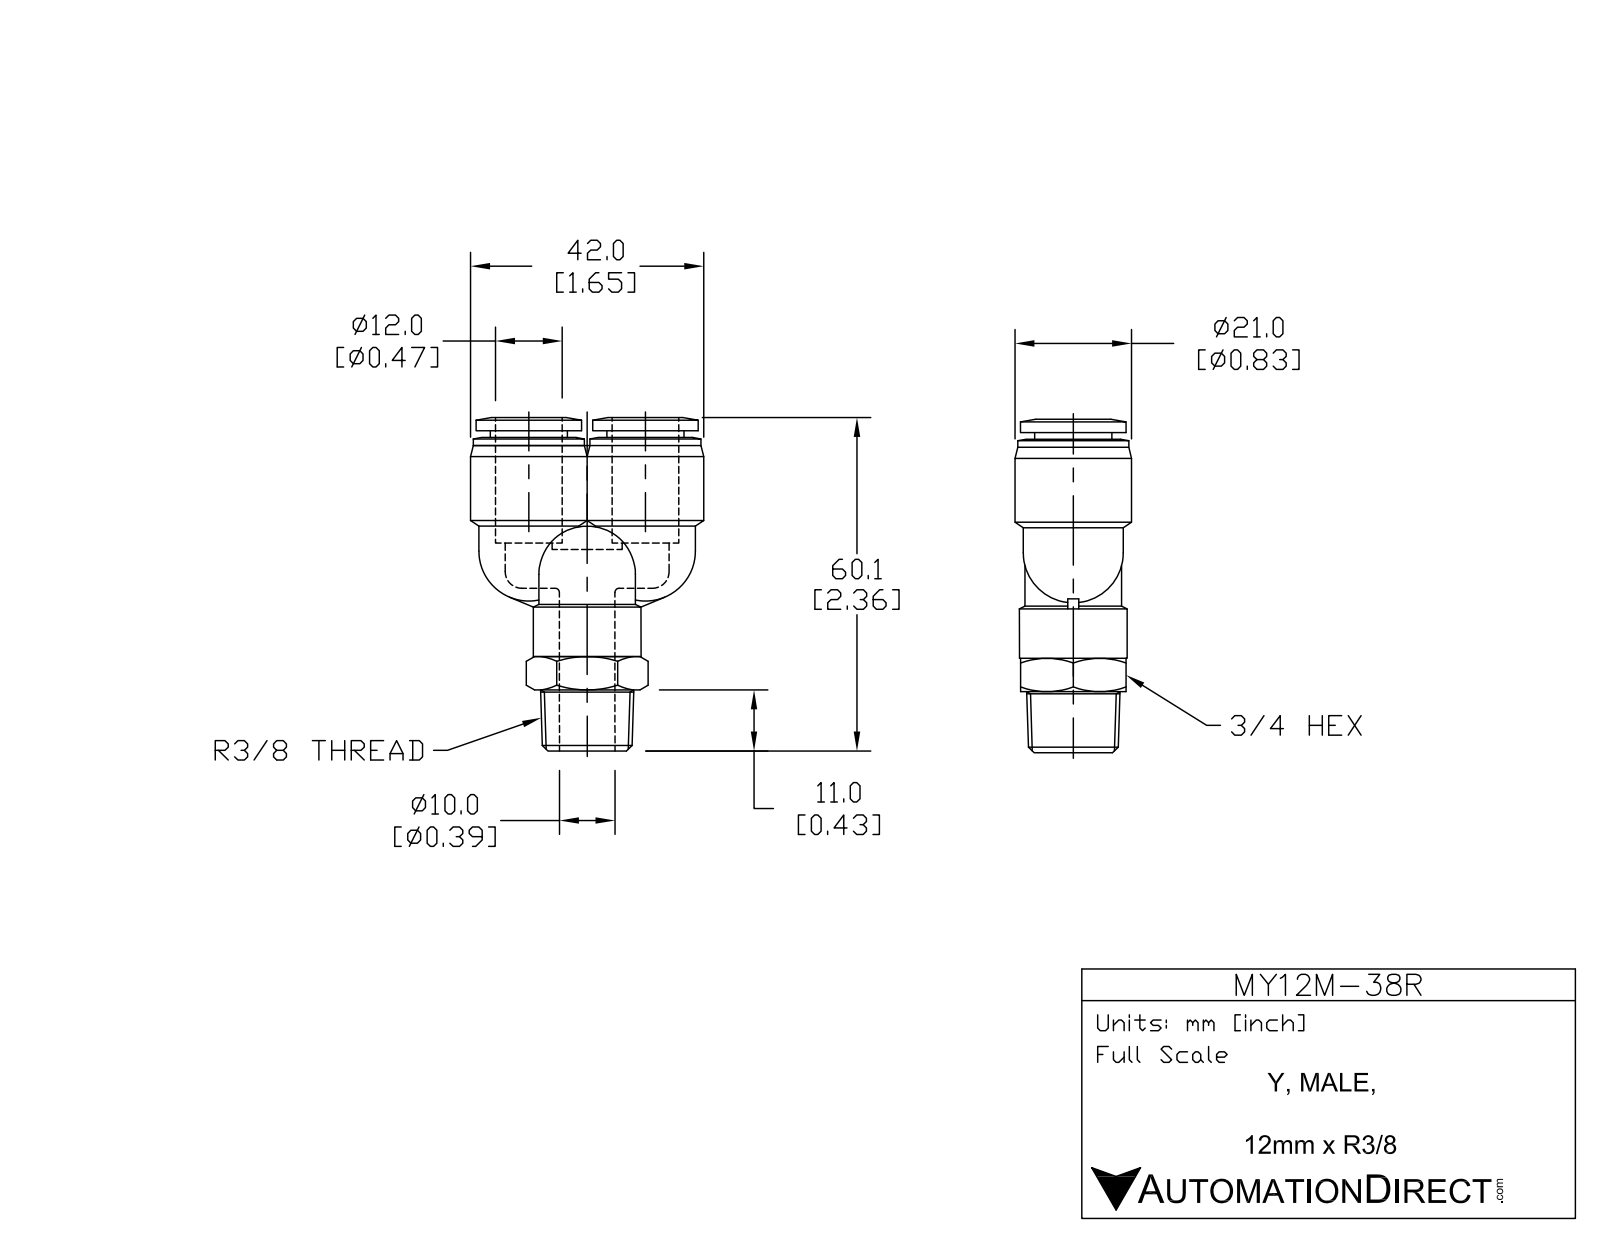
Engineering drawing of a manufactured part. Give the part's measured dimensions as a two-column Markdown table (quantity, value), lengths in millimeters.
| quantity | value |
| --- | --- |
| part name | MY12M-38R |
| STEP written by | SolidWorks 2015 (AUTOMOTIVE_DESIGN) |
| units | millimeters |
| bodies | 1 solid, 107 faces (24 planar, 34 cylindrical, 49 other) |
| overall size | 60.1 × 42 × 21 |
| volume | 16 630 mm³ |
| surface area | 10 140 mm² |
| round holes (diameter × count) | 10 × 4, 12.3 × 2 |
| round bosses / shafts (diameter × count) | 21 × 2, 20 × 2, 19 × 2, 18 × 2, 13.9 × 2, 19.4 × 1, 17.4 × 1 |
| main face-to-face distances | 19, 1.2, 19.1, 20.3, 37.4, 56.5, 57.8, 11, 26.4, 45.5 |
| hole center spacings | 10.5, 21 |
